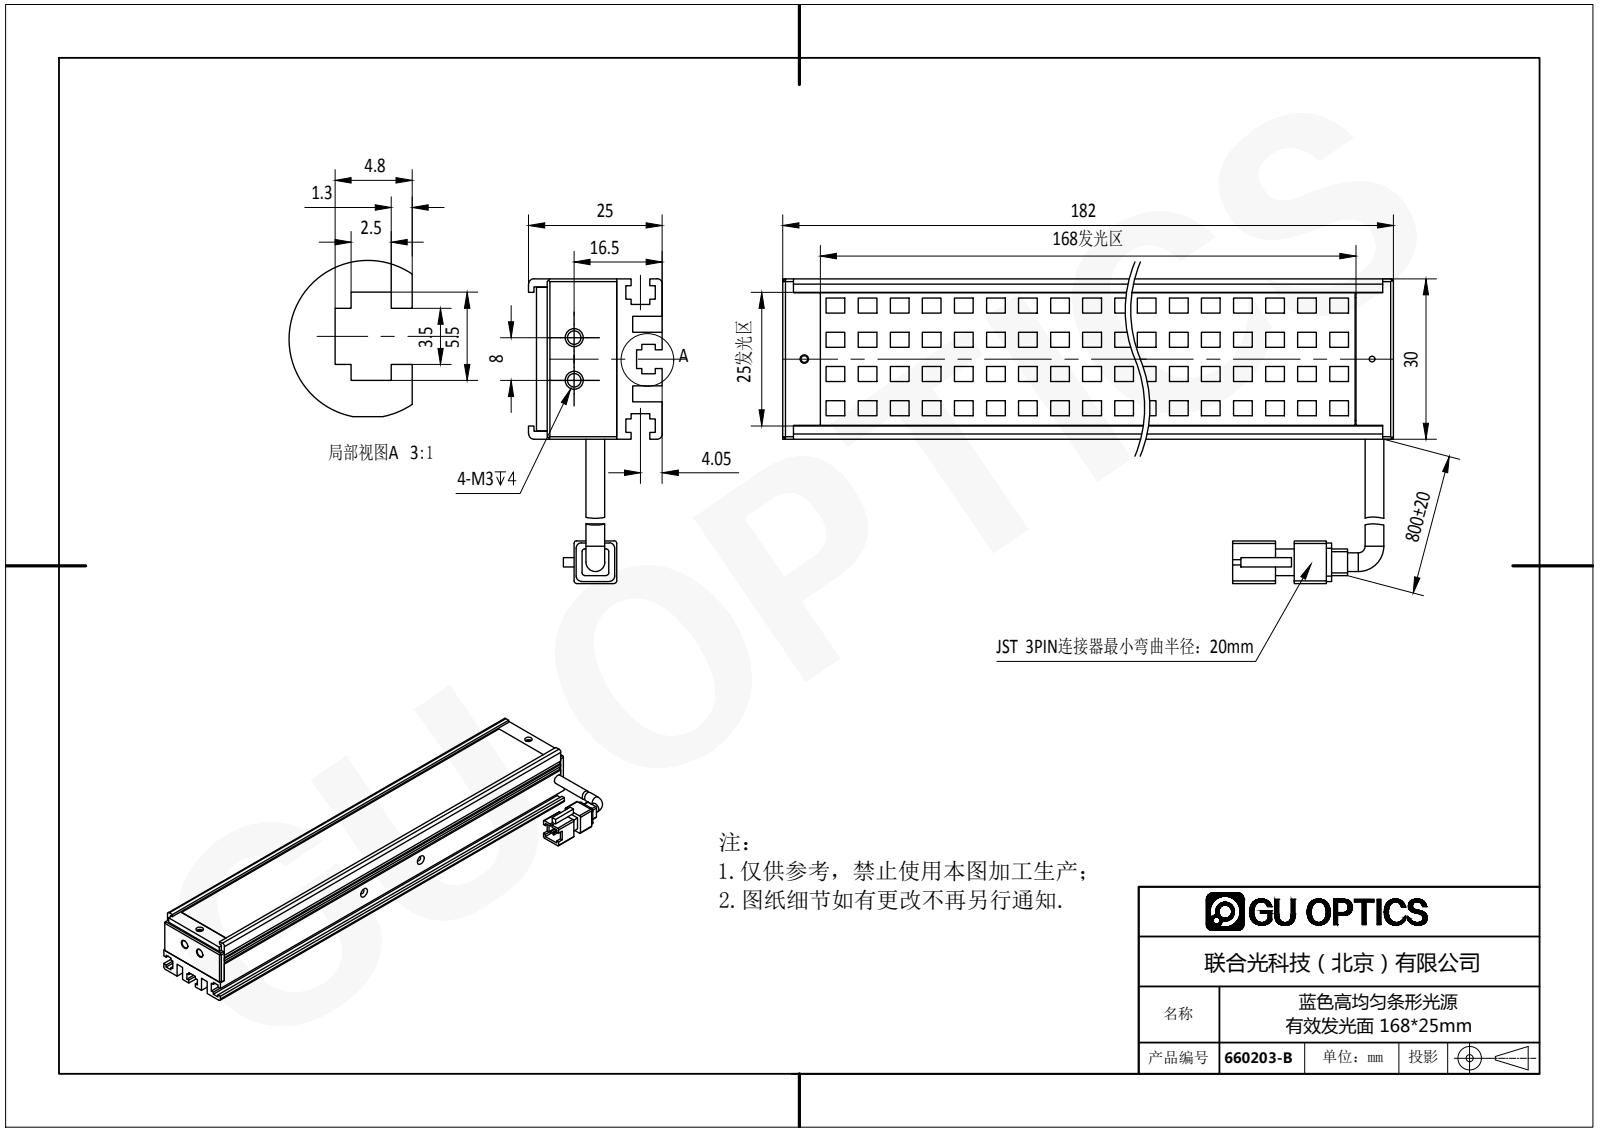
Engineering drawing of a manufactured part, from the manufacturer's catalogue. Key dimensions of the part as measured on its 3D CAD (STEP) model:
Part name (STEP PRODUCT): 660203-B
STEP written by: SolidWorks 2016 (AUTOMOTIVE_DESIGN)
Units: millimetres
Bodies: 6 solids, 1004 faces (818 planar, 83 cylindrical, 103 other)
Overall size (bounding box): 182 × 57 × 25
Volume: 63 499 mm³ · Surface area: 64 448 mm²
Round holes (diameter × count): ⌀1.6 ×5, ⌀1.5 ×2, ⌀1.7 ×2, ⌀2.5 ×2, ⌀2.8 ×2, ⌀3 ×2, ⌀1.1 ×1, ⌀1.25 ×1, ⌀2 ×1
Round bosses / shafts (diameter × count): ⌀3.5 ×2
Partial cylindrical surfaces — rounded edges, fillets, slot ends (radius × count): R1 ×12, R0.5 ×8, R1.65 ×1
Main face-to-face distances: 1, 13, 2, 2.5, 3, 9.5, 27.5, 4.5, 12, 8.5
Hole centre spacings: 174, 7, 72, 72.3, 102, 102.21, 174.14, 8
